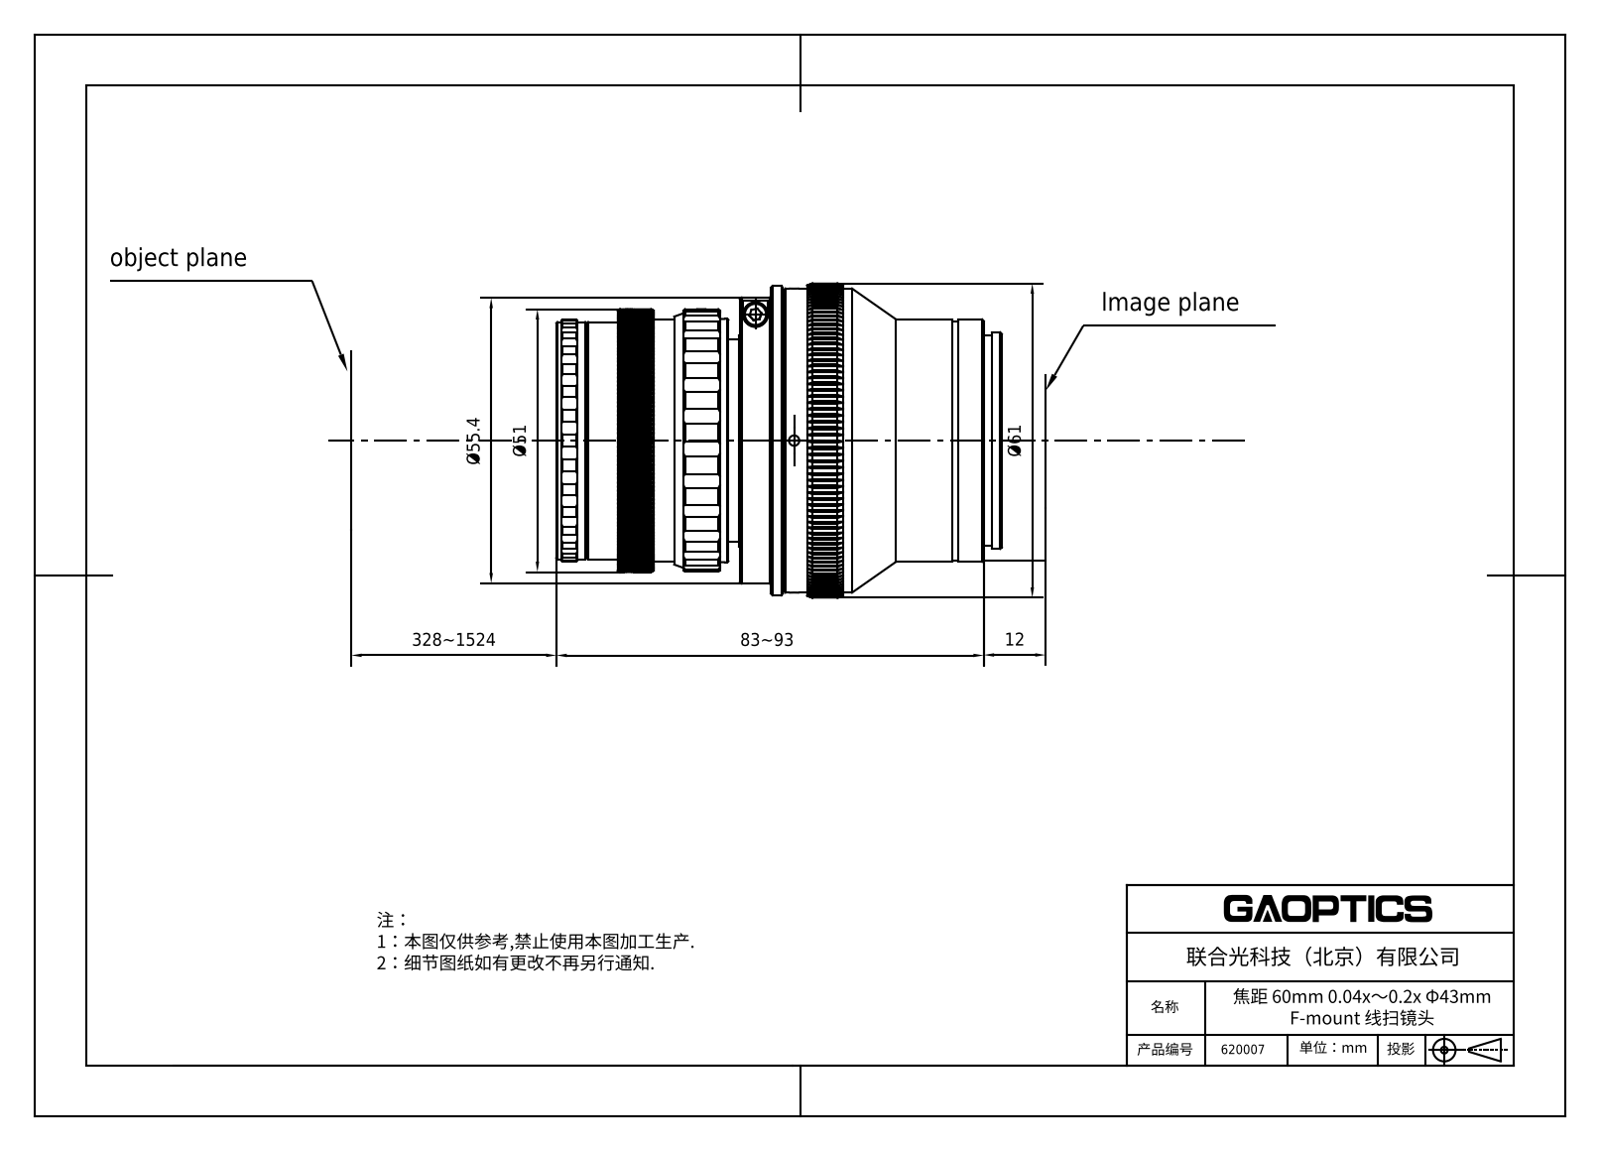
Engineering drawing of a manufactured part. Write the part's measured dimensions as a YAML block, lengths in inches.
part_name: "E1; M2.5x5 平头顶丝; G1 圧圈; M2.5x10_格立森 (+8 more)"
step_written_by: "SolidWorks 2016 (AUTOMOTIVE_DESIGN)"
units: inches
bodies: {solids: 21, faces: 2922, planar: 940, cylindrical: 1002, other: 980}
overall_size: [3.403, 2.402, 2.402]
volume: 5.98
surface_area: 115.7
round_holes:
  - {diameter: 0.079, count: 5}
  - {diameter: 0.051, count: 2}
  - {diameter: 0.055, count: 1}
  - {diameter: 0.102, count: 1}
  - {diameter: 0.433, count: 1}
  - {diameter: 0.504, count: 1}
  - {diameter: 0.637, count: 1}
  - {diameter: 0.709, count: 1}
  - {diameter: 0.827, count: 1}
  - {diameter: 0.835, count: 1}
  - {diameter: 0.945, count: 1}
  - {diameter: 1, count: 1}
round_bosses_or_shafts:
  - {diameter: 0.098, count: 2}
  - {diameter: 0.079, count: 2}
  - {diameter: 2.362, count: 1}
  - {diameter: 2.323, count: 1}
  - {diameter: 2.181, count: 1}
  - {diameter: 2.126, count: 1}
  - {diameter: 2.047, count: 1}
  - {diameter: 1.858, count: 1}
partial_cylinders:
  - {radius: 0.006, count: 180}
  - {radius: 0.098, count: 55}
  - {radius: 0.039, count: 7}
  - {radius: 0.197, count: 4}
  - {radius: 0.049, count: 2}
  - {radius: 0.03, count: 1}
  - {radius: 0.069, count: 1}
  - {radius: 0.094, count: 1}
face_to_face_distances: [0.177, 0.236, 0.504, 0.268, 0.691, 0.424, 0.098, 0.836, 1.072, 1.34]
hole_center_spacings: [0.65, 0.157, 0.552, 0.553, 0.709, 0.711, 1.262, 1.299]
